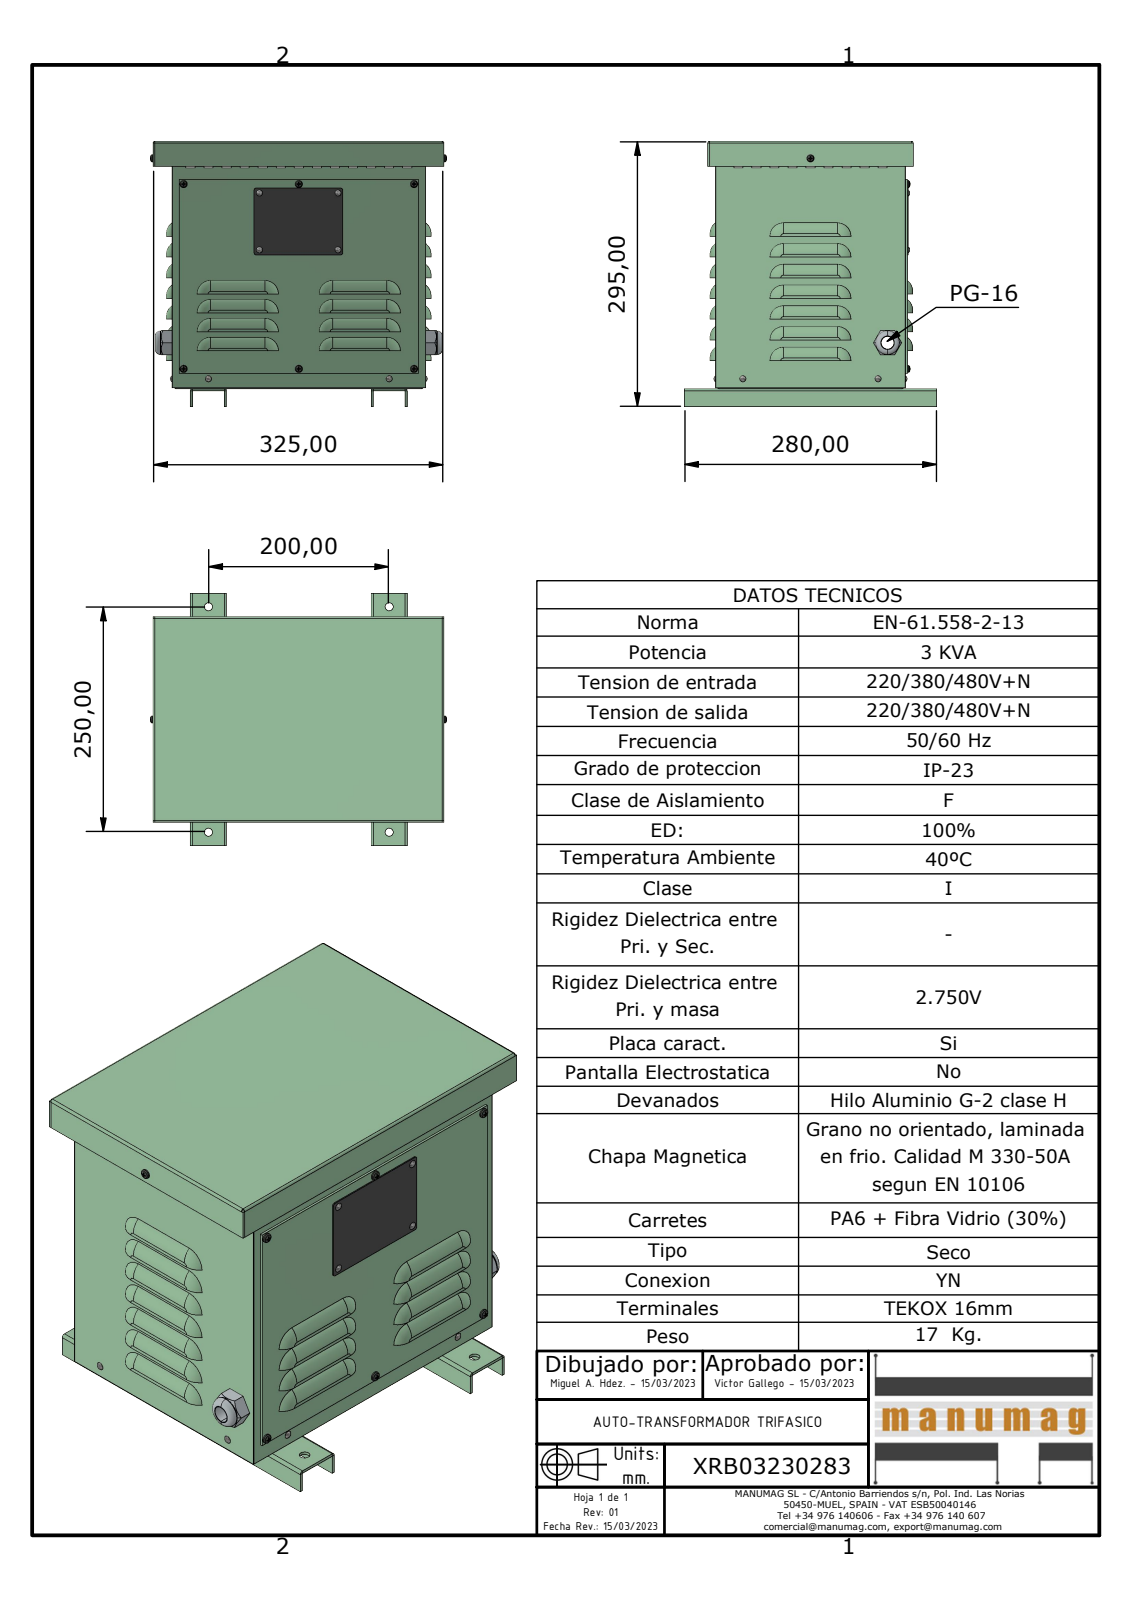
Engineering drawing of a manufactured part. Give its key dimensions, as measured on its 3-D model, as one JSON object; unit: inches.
{"part_name": "XRB03230283; JE003 - JE004 - JE005 EXPORT BASE; JE003 - JE004 - JE005 EXPORT PATA; JE003 - JE004 - JE005 EXPORT CUERPO (+6 more)", "step_written_by": "Autodesk Inventor 2023 (AUTOMOTIVE_DESIGN)", "units": "inches", "bodies": {"solids": 29, "faces": 1436, "planar": 841, "cylindrical": 283, "other": 312}, "overall_size": [12.919, 11.594, 11.024], "volume_in3": 50.51, "surface_area_in2": 1645, "round_holes": [[0.189, 13], [0.118, 12], [0.354, 6], [0.15, 5], [0.157, 4], [0.551, 1], [0.945, 1]], "round_bosses_or_shafts": [[0.126, 8], [0.157, 7], [0.143, 7], [1.024, 1], [0.906, 1], [0.886, 1]], "partial_cylinders_radius": [[0.551, 44], [0.157, 25], [0.591, 25], [0.02, 9], [0.079, 8], [0.177, 8], [0.059, 6], [0.059, 4]], "face_to_face_distances": [0.02, 0.079, 8.287, 11.043, 0.098, 0.059, 10.807, 10.728, 8.307, 8.386], "hole_center_spacings": [5.02, 7.874, 9.505, 8.071, 1.166, 1.757, 1.85, 2.48]}
